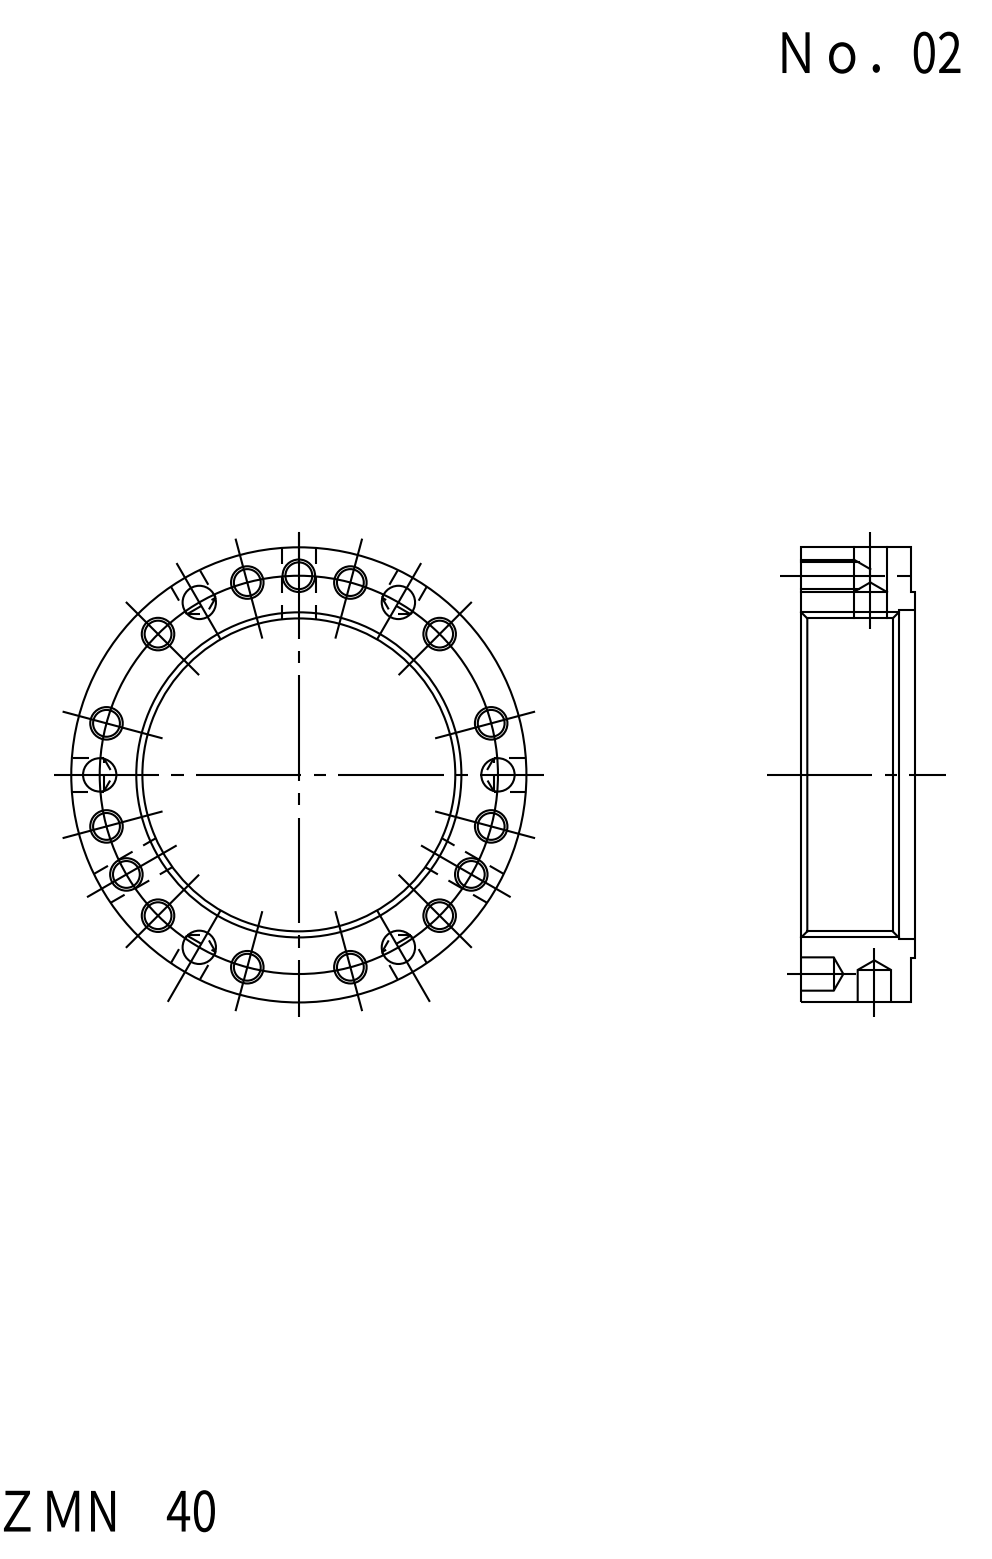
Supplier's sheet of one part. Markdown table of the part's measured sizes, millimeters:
| quantity | value |
| --- | --- |
| part name | FKD ZMN40 |
| STEP written by | Autodesk Inventor LT (CONFIG_CONTROL_DESIGN) |
| units | millimeters |
| bodies | 1 solid, 62 faces (4 planar, 34 cylindrical, 24 other) |
| overall size | 56 × 56 × 14 |
| volume | 14 353 mm³ |
| surface area | 8 704 mm² |
| round holes (diameter × count) | 3.24 × 15, 4.1 × 12, 40 × 1, 40.5 × 1 |
| round bosses / shafts (diameter × count) | 56 × 1, 45 × 1 |
| main face-to-face distances | 13.5, 0.5, 14, 1.5, 1, 12.5 |
| hole center spacings | 24.5, 42.44, 29.83, 12.68, 34.65, 47.33, 6.4, 18.75 |
